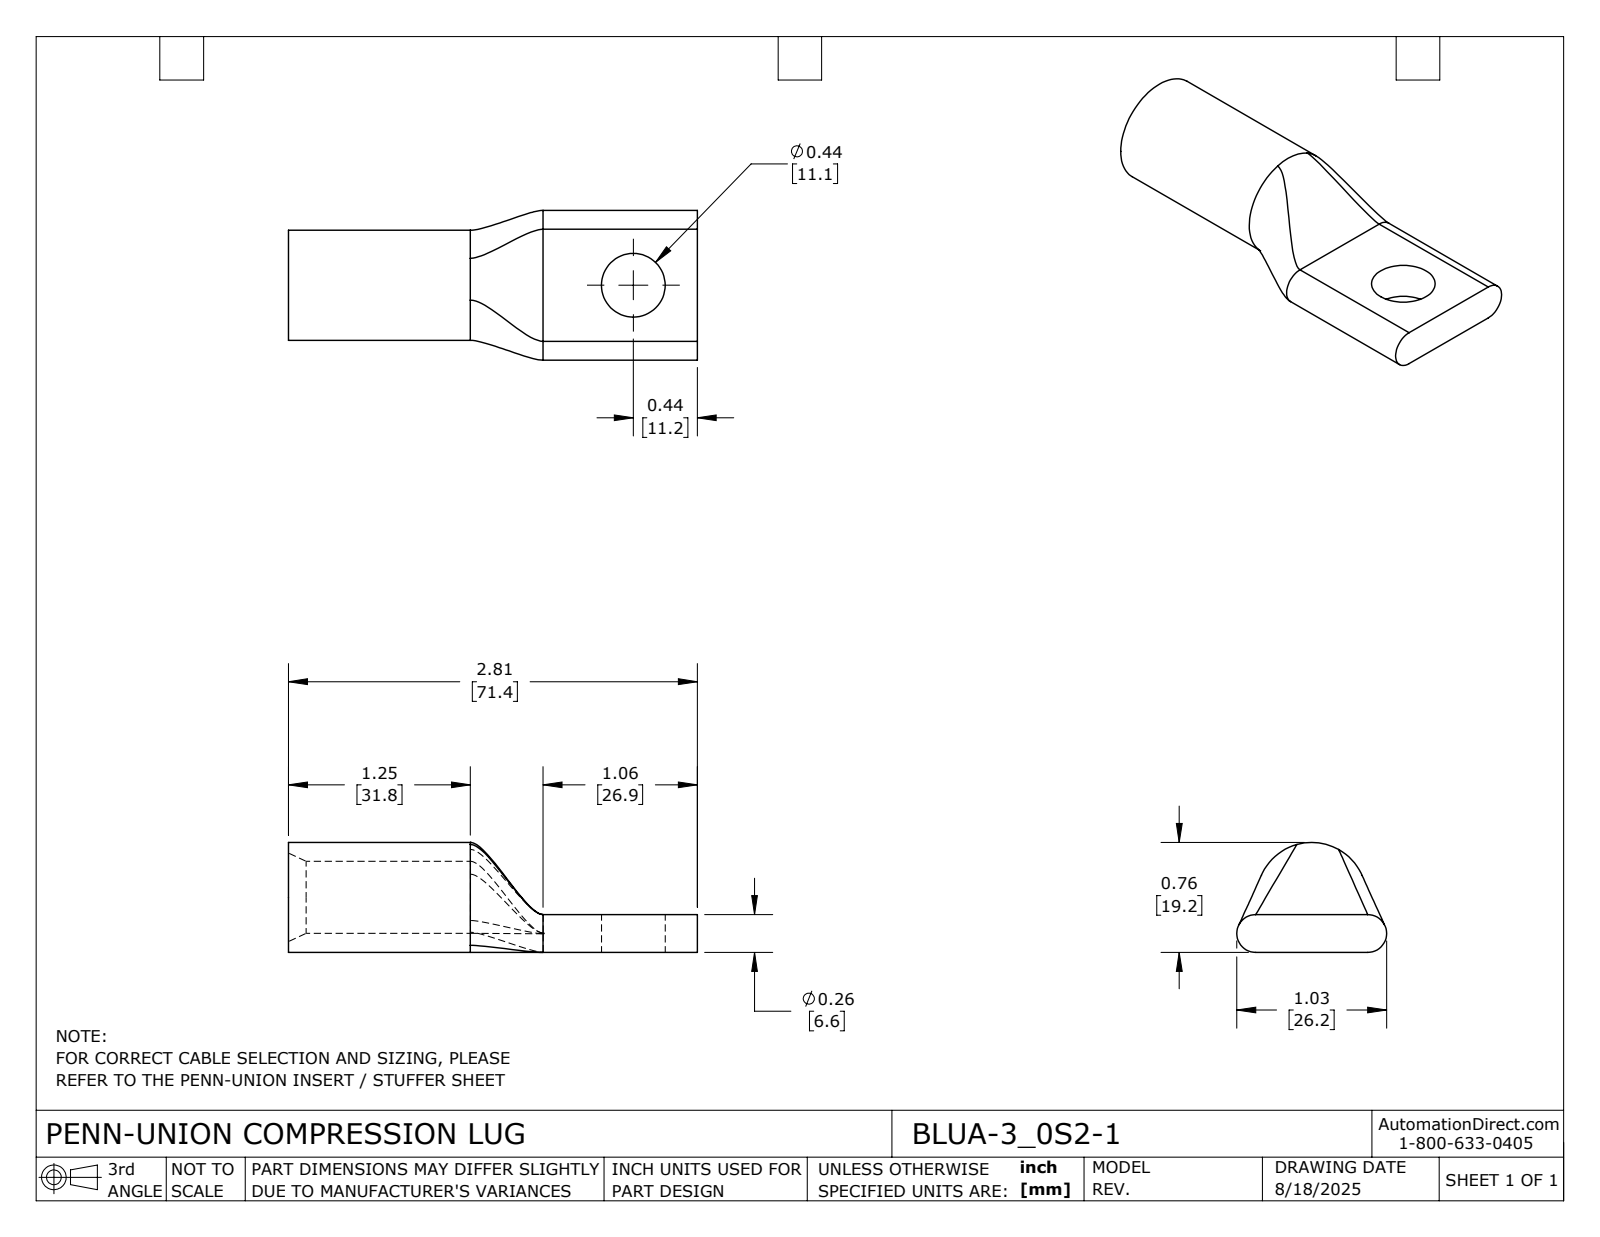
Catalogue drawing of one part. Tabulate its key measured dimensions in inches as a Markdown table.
| quantity | value |
| --- | --- |
| part name | BLUA-3_0S2-1 |
| STEP written by | SolidWorks 2024 (CONFIG_CONTROL_DESIGN) |
| units | inches |
| bodies | 1 solid, 24 faces (5 planar, 9 cylindrical, 10 other) |
| overall size | 2.81 × 1.03 × 0.756 |
| volume | 0.671 in³ |
| surface area | 10.13 in² |
| round holes (diameter × count) | 0.438 × 1, 0.495 × 1 |
| round bosses / shafts (diameter × count) | 0.756 × 1 |
| partial cylindrical surfaces (radius × count) | 0.13 × 2 |
| main face-to-face distances | 0.26, 2.81, 1.75, 1.06 |
